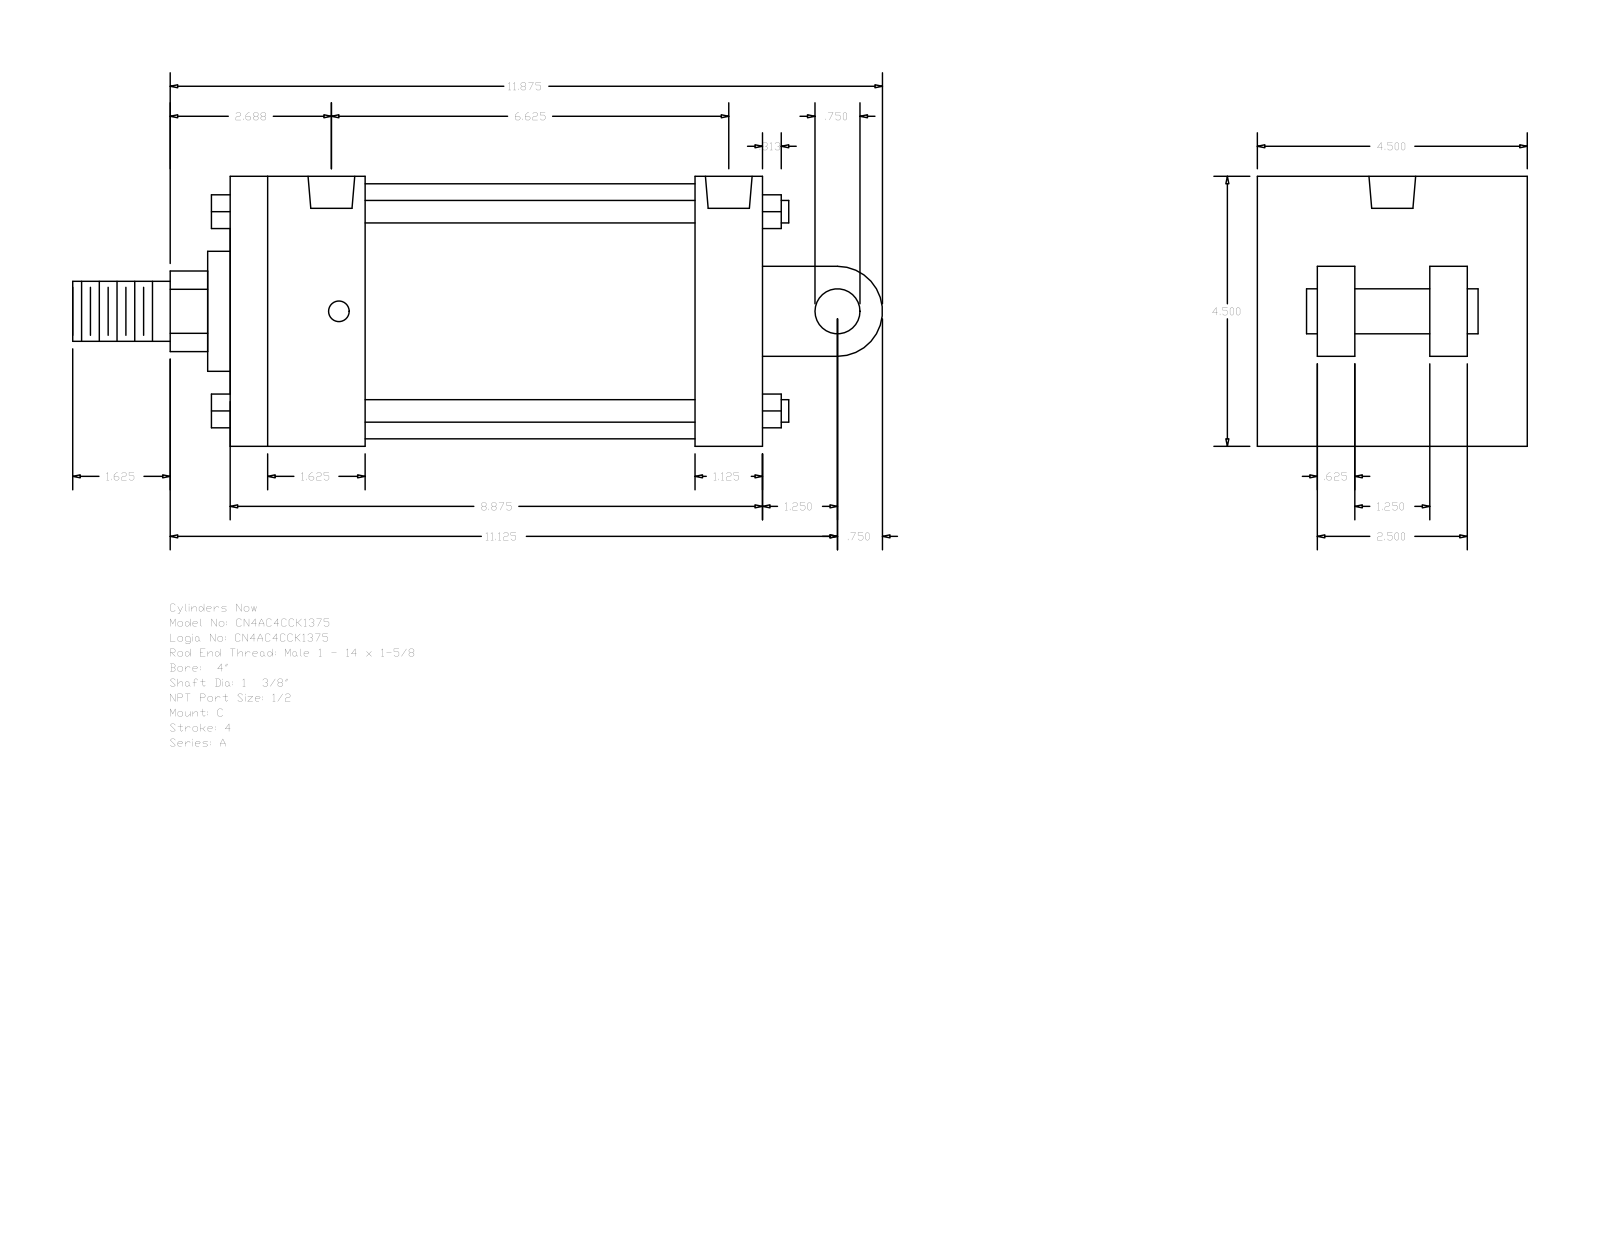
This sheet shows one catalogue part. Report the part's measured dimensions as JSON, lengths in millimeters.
{"part_name": "A_C__0400_1.375", "step_written_by": "GSSL Pune (CONFIG_CONTROL_DESIGN)", "units": "millimeters", "bodies": {"solids": 0, "faces": 135, "planar": 102, "cylindrical": 33, "other": 0}, "overall_size": [342.9, 114.3, 114.3], "round_holes": [[8.73, 4], [19.77, 2]], "round_bosses_or_shafts": [[9.53, 4], [107.95, 1], [50.8, 1], [34.92, 1], [25.4, 1], [19.05, 1]], "partial_cylinders_radius": [[17.06, 1], [19.05, 1]], "face_to_face_distances": [114.3, 225.42, 57.15, 73.03, 196.85, 28.57, 139.7, 168.27, 41.27, 25.4], "hole_center_spacings": [3.18, 161.92, 165.1, 168.28]}
